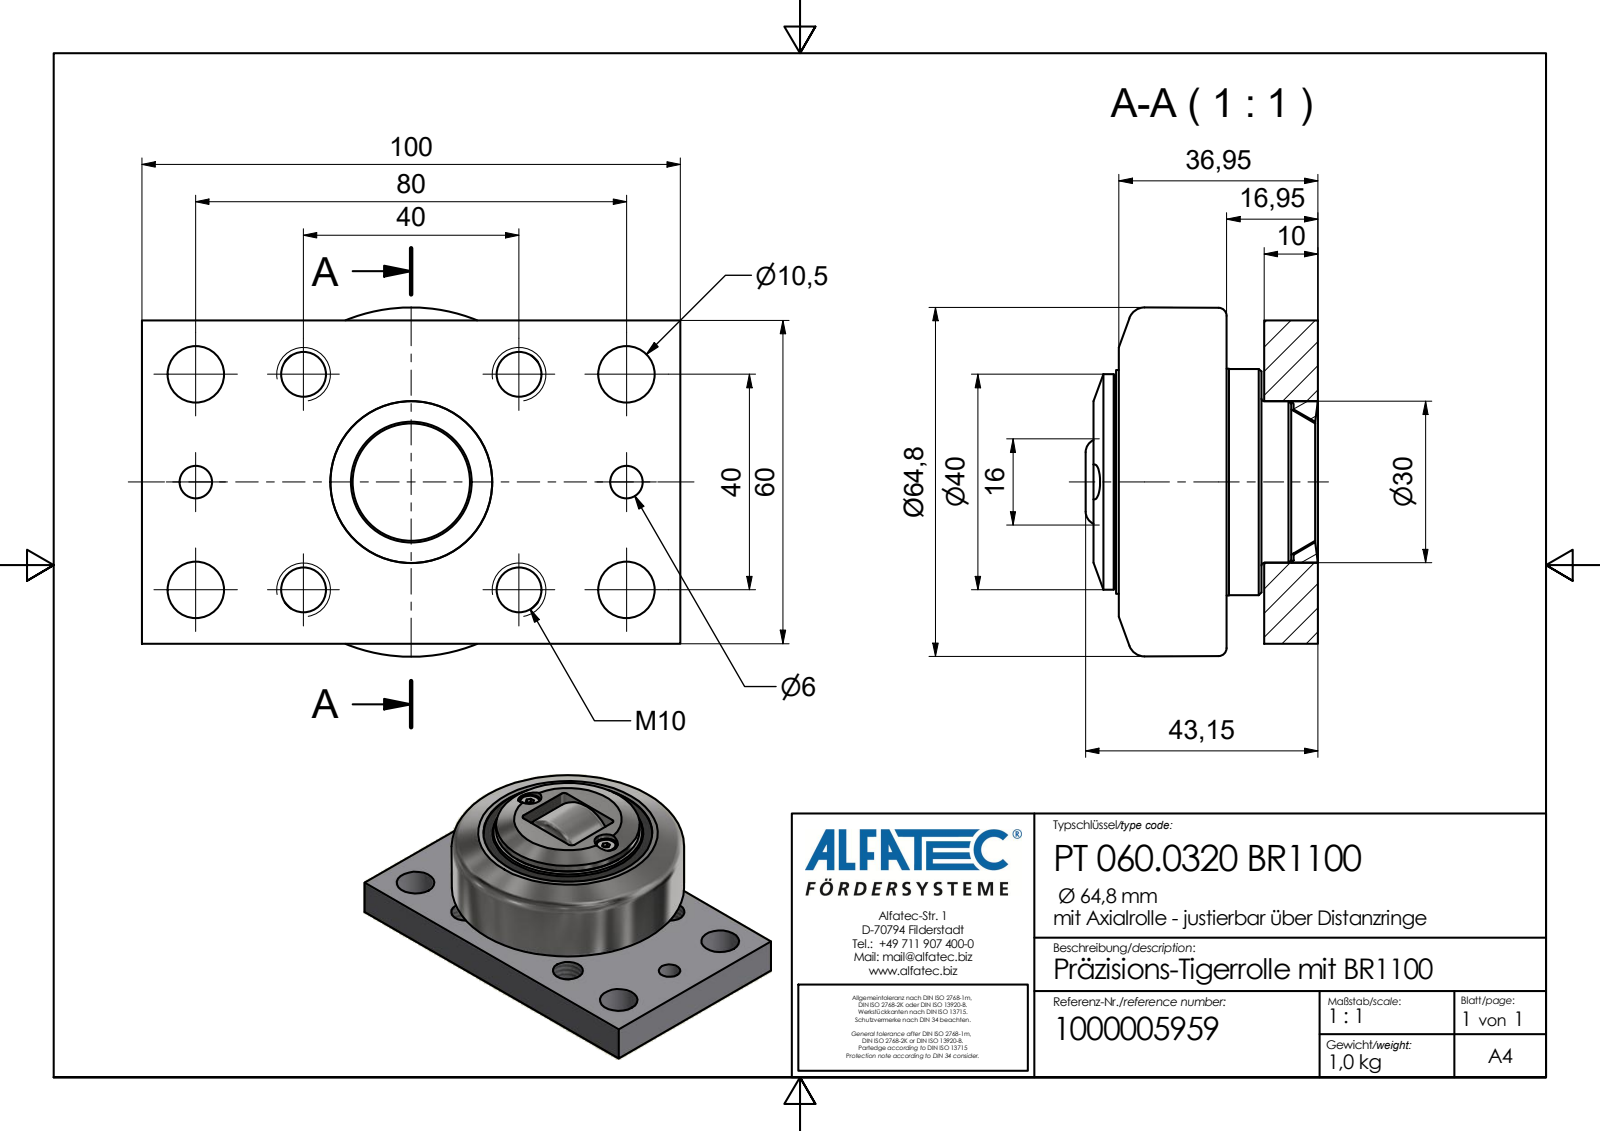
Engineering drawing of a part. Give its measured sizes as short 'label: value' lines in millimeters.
name: PT 060.0320 BR1100_Kontur
written by: Autodesk Inventor 2020 (AP242_MANAGED_MODEL_BASED_3D_ENGINEERING_MIM_LF)
unit: mm
bodies: 1 solid, 125 faces (51 planar, 46 cylindrical, 28 other)
size: 100 × 64.8 × 43.15
volume: 128 765 mm³; area: 32 057 mm²
holes: 4× ⌀8.38, 4× ⌀10.5, 2× ⌀3.4, 2× ⌀6, 2× ⌀6.5, 1× ⌀10.2, 1× ⌀13, 1× ⌀16, 1× ⌀38, 1× ⌀42, 1× ⌀42.97, 1× ⌀47
bosses: 2× ⌀5.35, 2× ⌀3, 1× ⌀42.1, 1× ⌀41.5, 1× ⌀40, 1× ⌀25, 1× ⌀11
rounds: 4× R1, 1× R12.47
face distances: 10, 16.95, 6.95, 60, 20.7, 37.65, 27.65, 20, 0.45, 100
hole spacings: 20, 28.28, 40, 44.72, 58.52, 20.62, 32.02, 40.31
